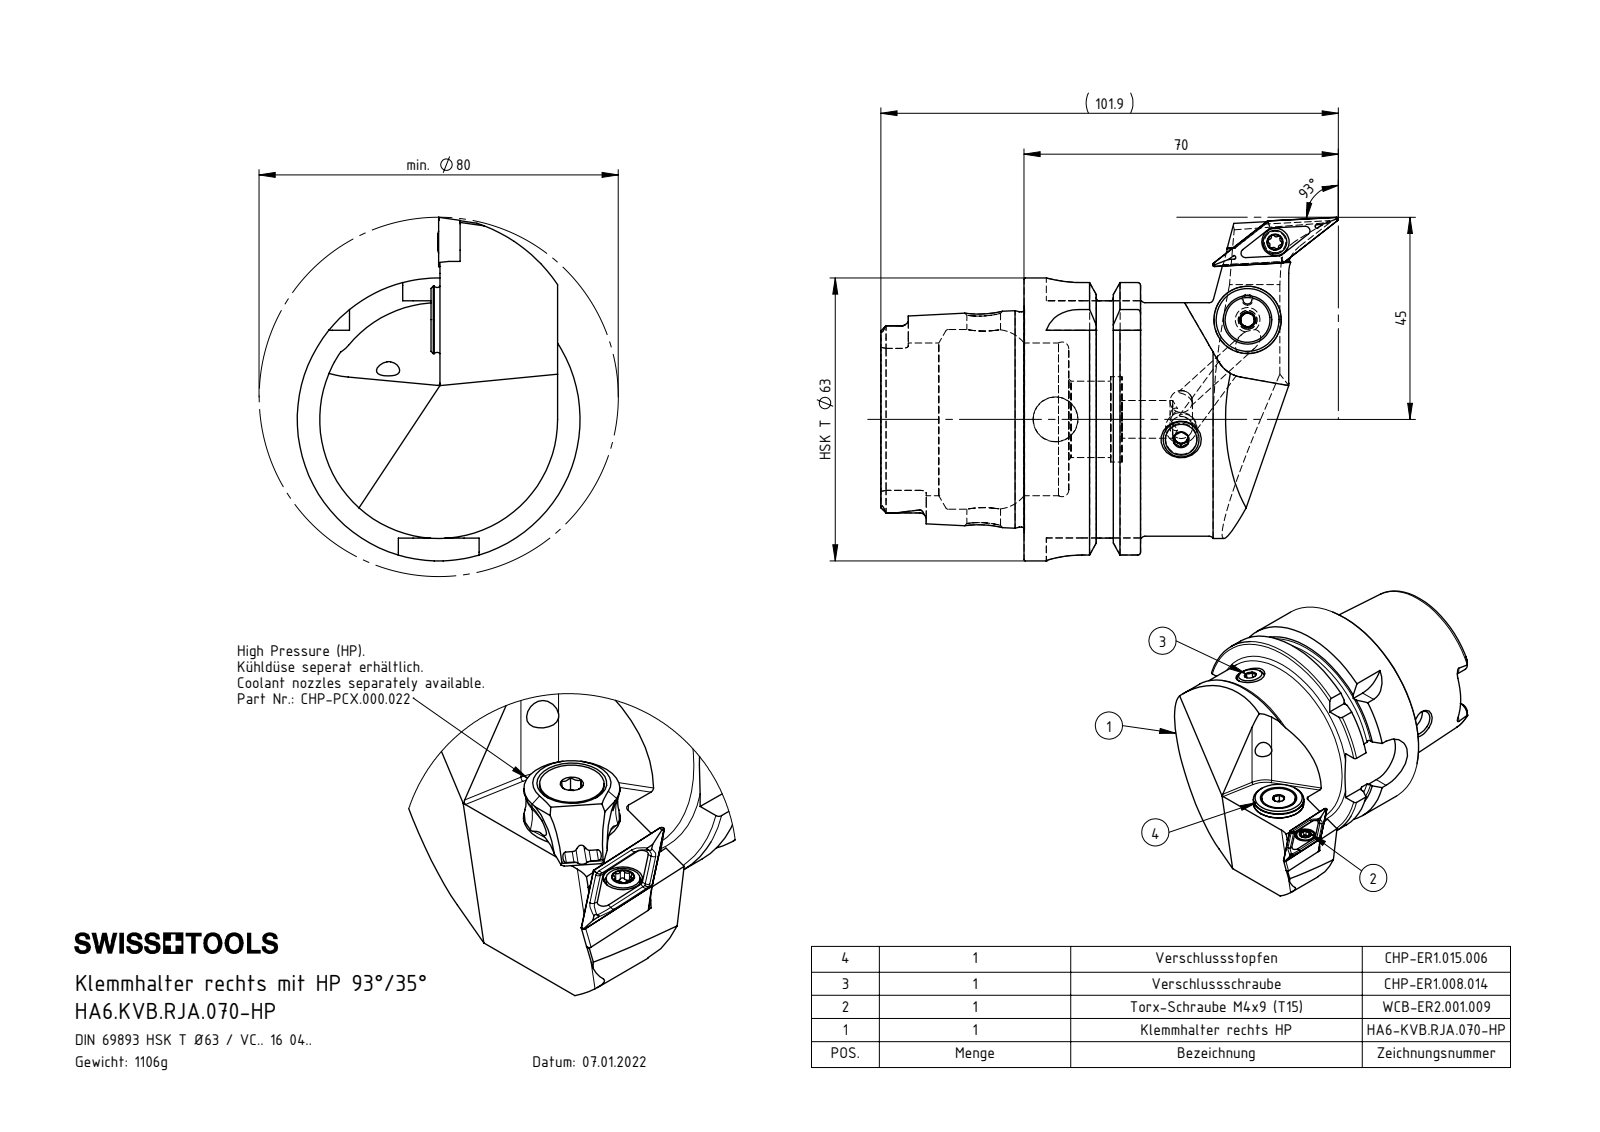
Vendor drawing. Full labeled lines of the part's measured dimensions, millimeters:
Part name (STEP PRODUCT): DIN 7991 - M5x18; DIN 3771 - 6.5x1.5; HA6-KVB.RJA.070-HP_A; CHP-PCX.000.022_Düse (+7 more)
STEP written by: SolidWorks 2022 (CONFIG_CONTROL_DESIGN)
Units: millimetres
Bodies: 9 solids, 519 faces (134 planar, 149 cylindrical, 236 other)
Overall size (bounding box): 101.9 × 76.5 × 63
Volume: 140 849 mm³ · Surface area: 33 502 mm²
Round holes (diameter × count): ⌀4.2 ×2, ⌀5 ×2, ⌀1.2 ×1, ⌀2 ×1, ⌀3 ×1, ⌀3.3 ×1, ⌀4.4 ×1, ⌀5.3 ×1, ⌀6.1 ×1, ⌀7 ×1, ⌀7.5 ×1, ⌀8.4 ×1
Round bosses / shafts (diameter × count): ⌀63 ×1, ⌀54.95 ×1, ⌀52 ×1, ⌀47.94 ×1, ⌀14.85 ×1, ⌀13.4 ×1, ⌀10 ×1, ⌀8 ×1
Partial cylindrical surfaces — rounded edges, fillets, slot ends (radius × count): R1 ×7, R0.34 ×6, R0.59 ×6, R1.4 ×6, R0.5 ×4, R8 ×4, R6 ×3, R1.1 ×2
Main face-to-face distances: 25.95, 16, 9.95, 31.9, 41.85, 57.85, 52.8, 21.8, 26.2, 11.85
Hole centre spacings: 4.5, 14.22, 14.3, 18.37, 18.44, 48.19, 50.38, 62.85
